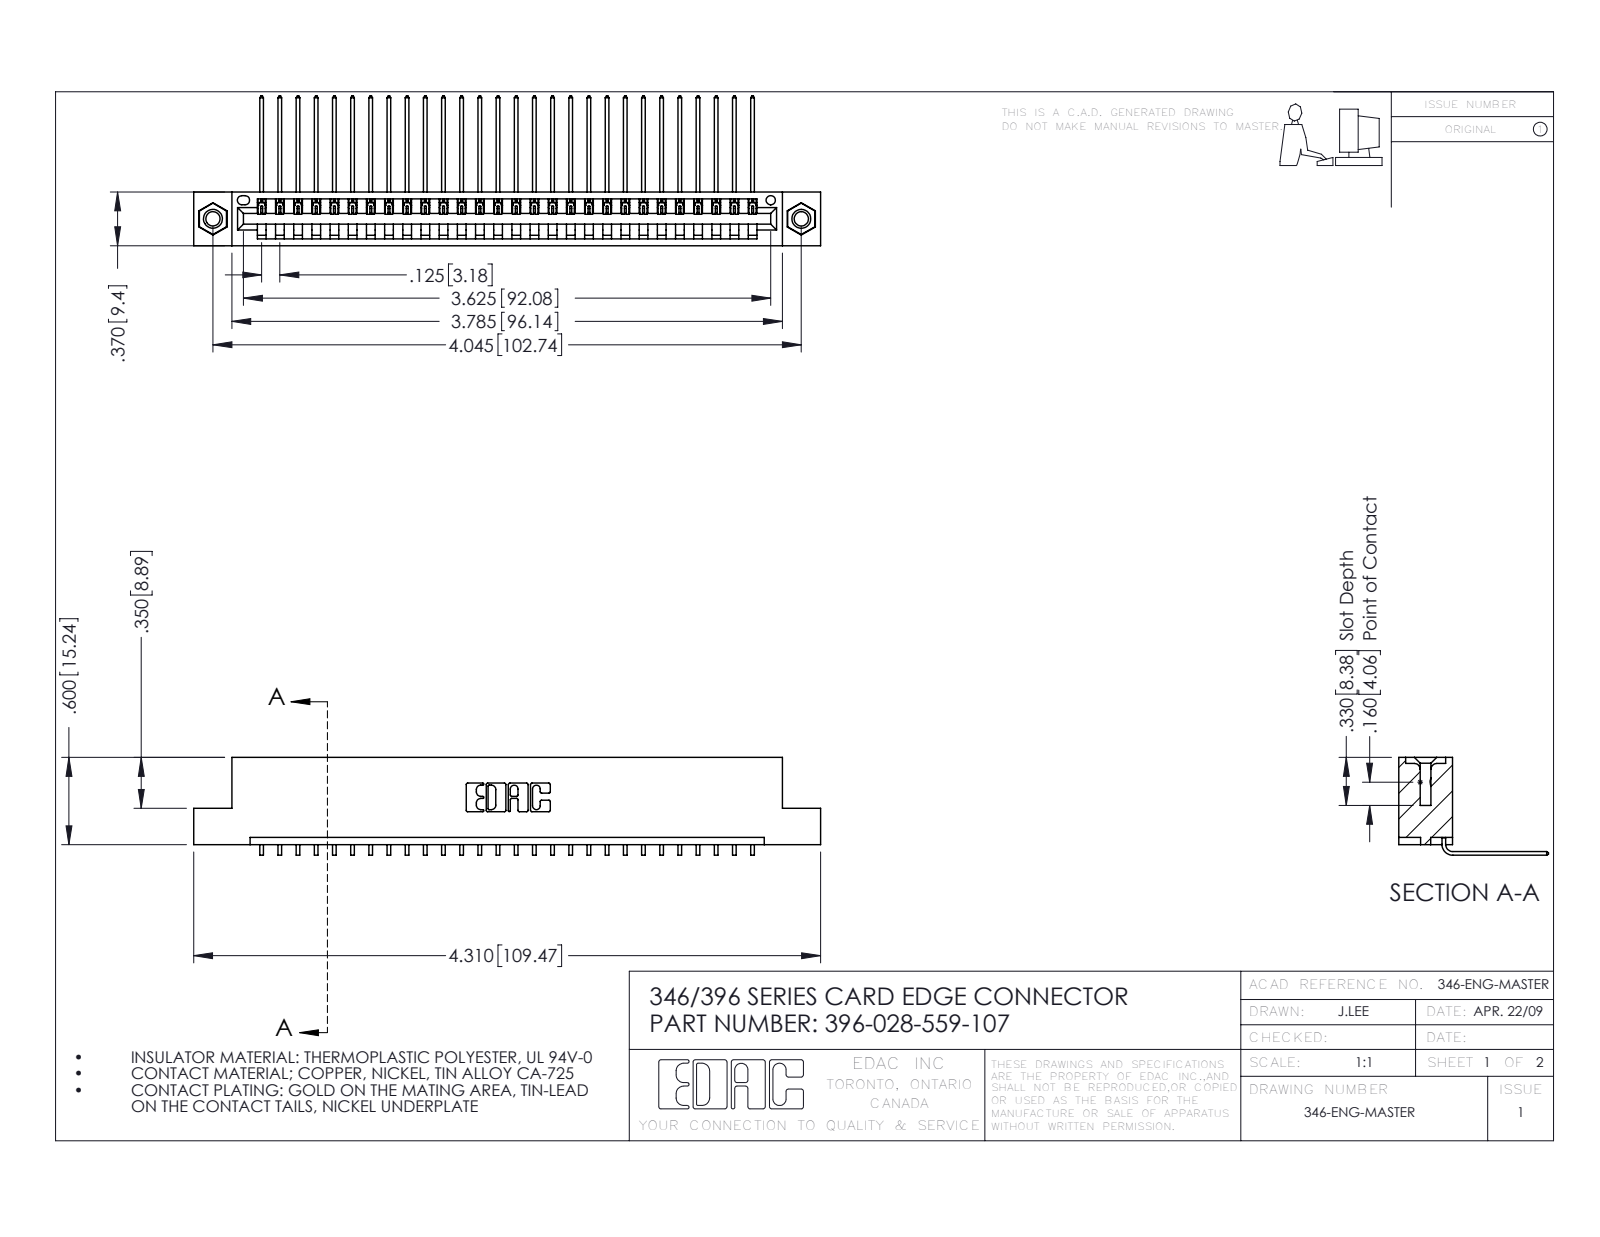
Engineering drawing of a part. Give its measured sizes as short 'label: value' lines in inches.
name: 345-250-001_345-250-005-103; 345-292-001_558 559 Tail - 1; 396-028-559-107; 346 Part_Flush Mounting Lugs - 0.156 Dia-TI
written by: SolidWorks 2016 (CONFIG_CONTROL_DESIGN)
unit: in
bodies: 31 solids, 1862 faces (1284 planar, 562 cylindrical, 16 other)
size: 4.31 × 1.03 × 0.673
volume: 0.638 in³; area: 20.95 in²
holes: 2× ⌀0.098, 2× ⌀0.125, 2× ⌀0.156, 1× ⌀0.064
bosses: 2× ⌀0.155
rounds: 56× R0.006, 22× R0.01, 6× R0.007, 6× R0.031, 3× R0.026, 2× R0.031, 2× R0.04, 1× R0.014
face distances: 0.048, 0.322, 0.37, 0.25, 0.072, 0.025, 0.298, 0.148, 0.222, 0.1
hole spacings: 0.246, 3.837, 4.045
